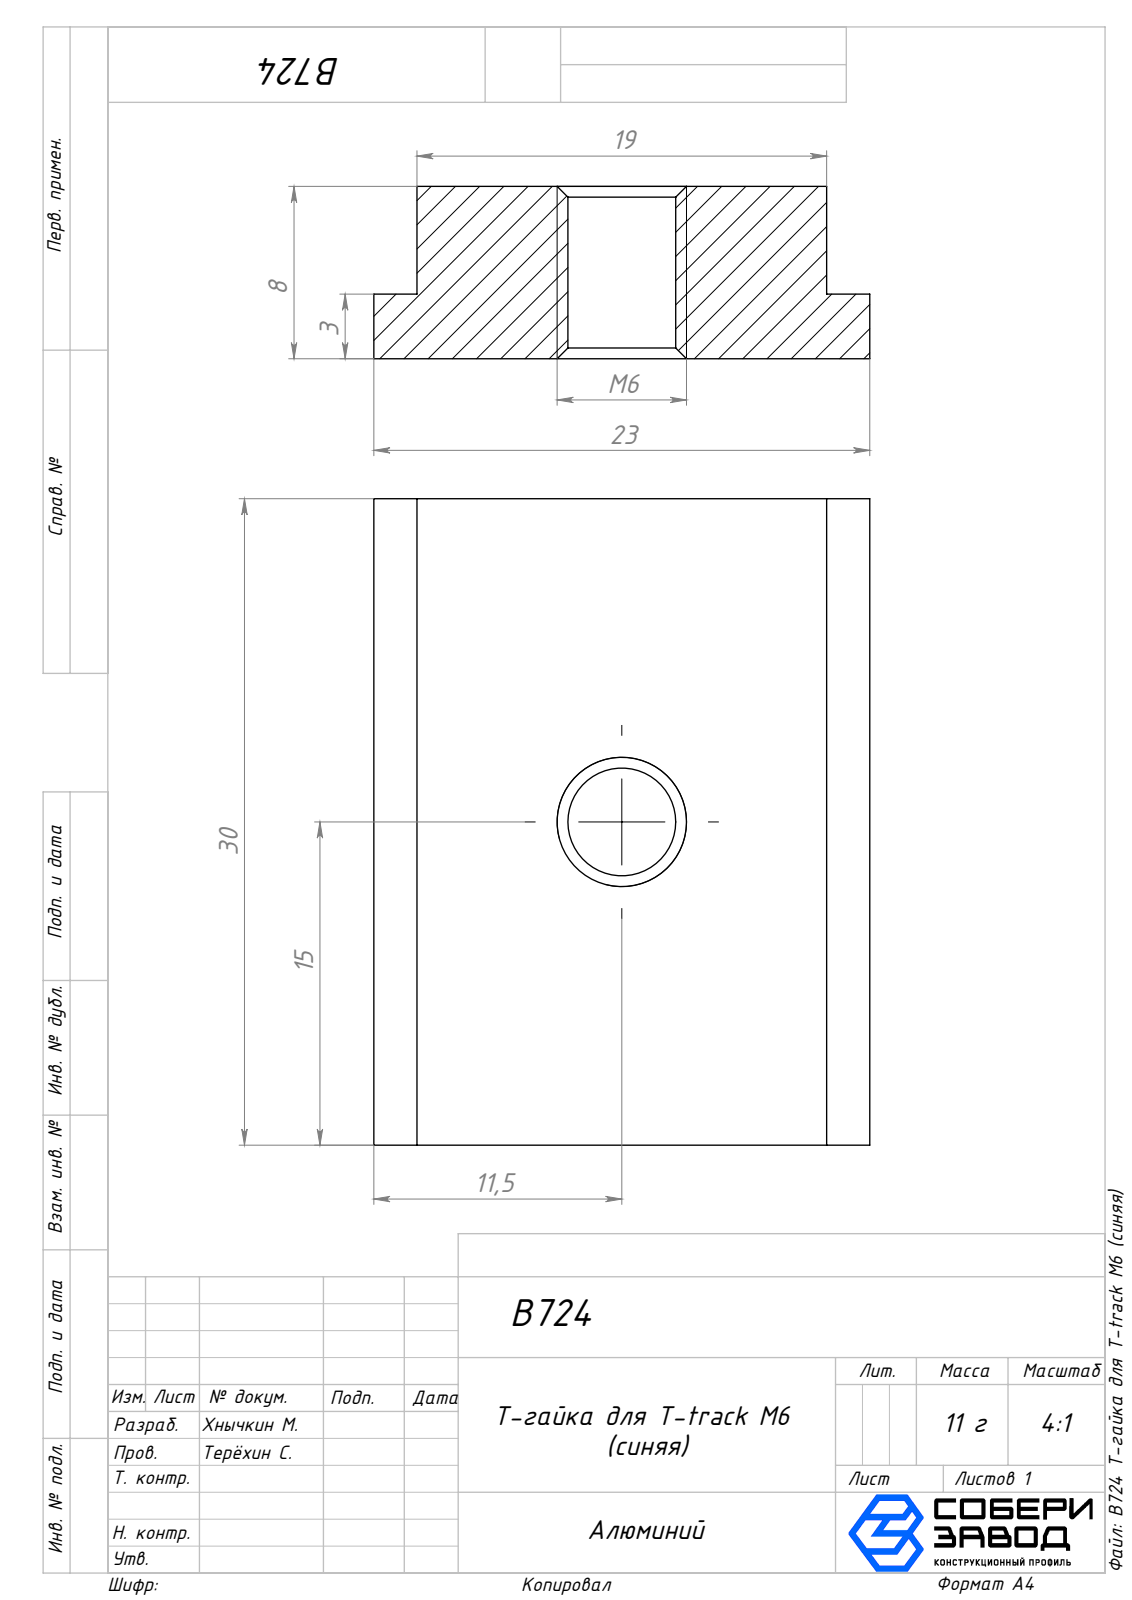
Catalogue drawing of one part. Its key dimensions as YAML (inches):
part_name: "B724 Т-гайка для T-track M6 (синяя)"
step_written_by: "SolidWorks 2025 (AUTOMOTIVE_DESIGN)"
units: inches
bodies: {solids: 1, faces: 16, planar: 10, cylindrical: 2, other: 4}
overall_size: [1.181, 0.906, 0.315]
volume: 0.29
surface_area: 3.512
round_holes:
  - {diameter: 0.197, count: 1}
face_to_face_distances: [0.315, 0.079, 0.827, 1.181, 0.748, 0.118, 0.197, 0.906]
